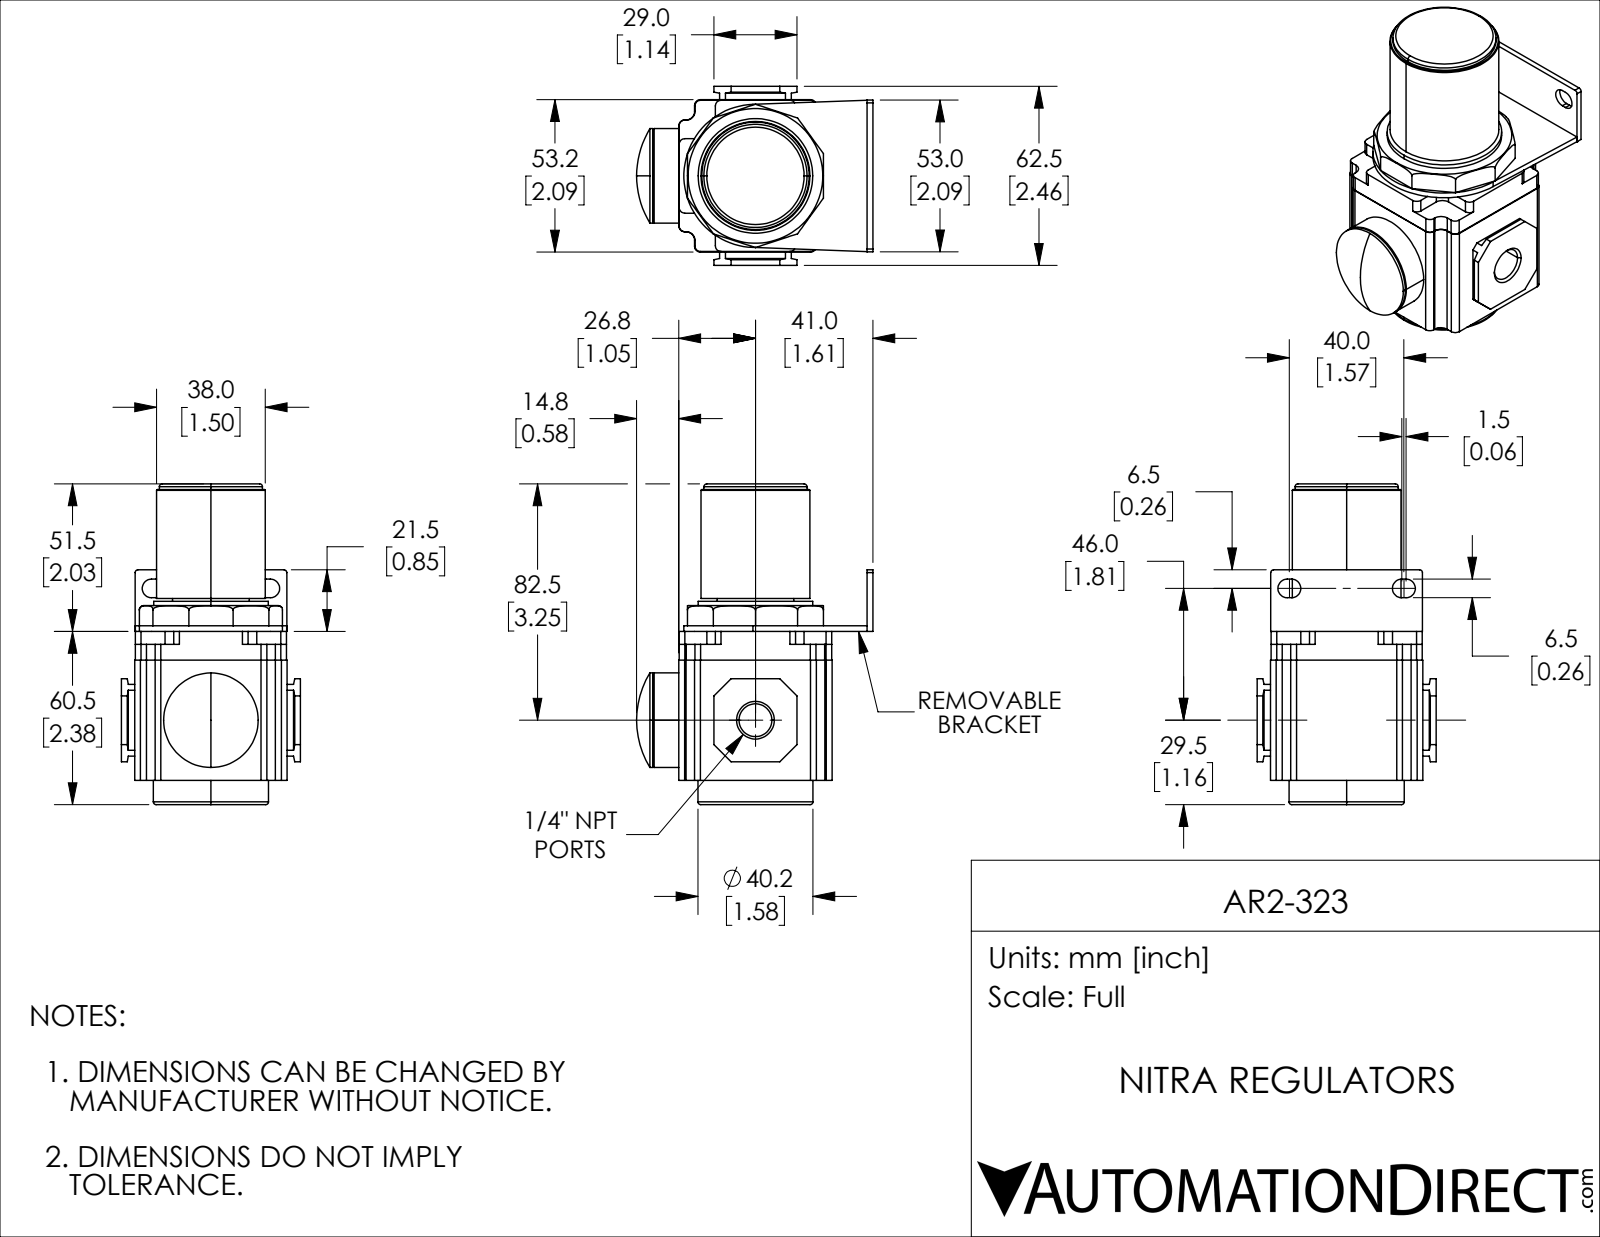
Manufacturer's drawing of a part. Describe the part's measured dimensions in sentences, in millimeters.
The part is named "AR2-323". Its 3-D file was written by "SolidWorks 2019 (CONFIG_CONTROL_DESIGN)". It is 1 solid with 188 faces: 111 planar, 61 cylindrical and 16 other. Overall it measures 112 by 82.5 by 62.5 millimeters. Its volume is 230 872 cubic millimeters and its surface area 32 362 square millimeters. Round holes: 1 of diameter 11.45. Round bosses or shafts: 1 of diameter 40.2, 1 of diameter 40, 1 of diameter 38, 1 of diameter 36, 1 of diameter 33, 1 of diameter 26.78. Partial cylindrical surfaces (rounded edges, fillets, slot ends): 24 of radius 2, 12 of radius 3, 4 of radius 3.25, 2 of radius 1, 1 of radius 25. The main face-to-face distances are 62.5, 2, 8.5, 54, 52, 4.65, 57.85, 14.25, 60.5, 56.
